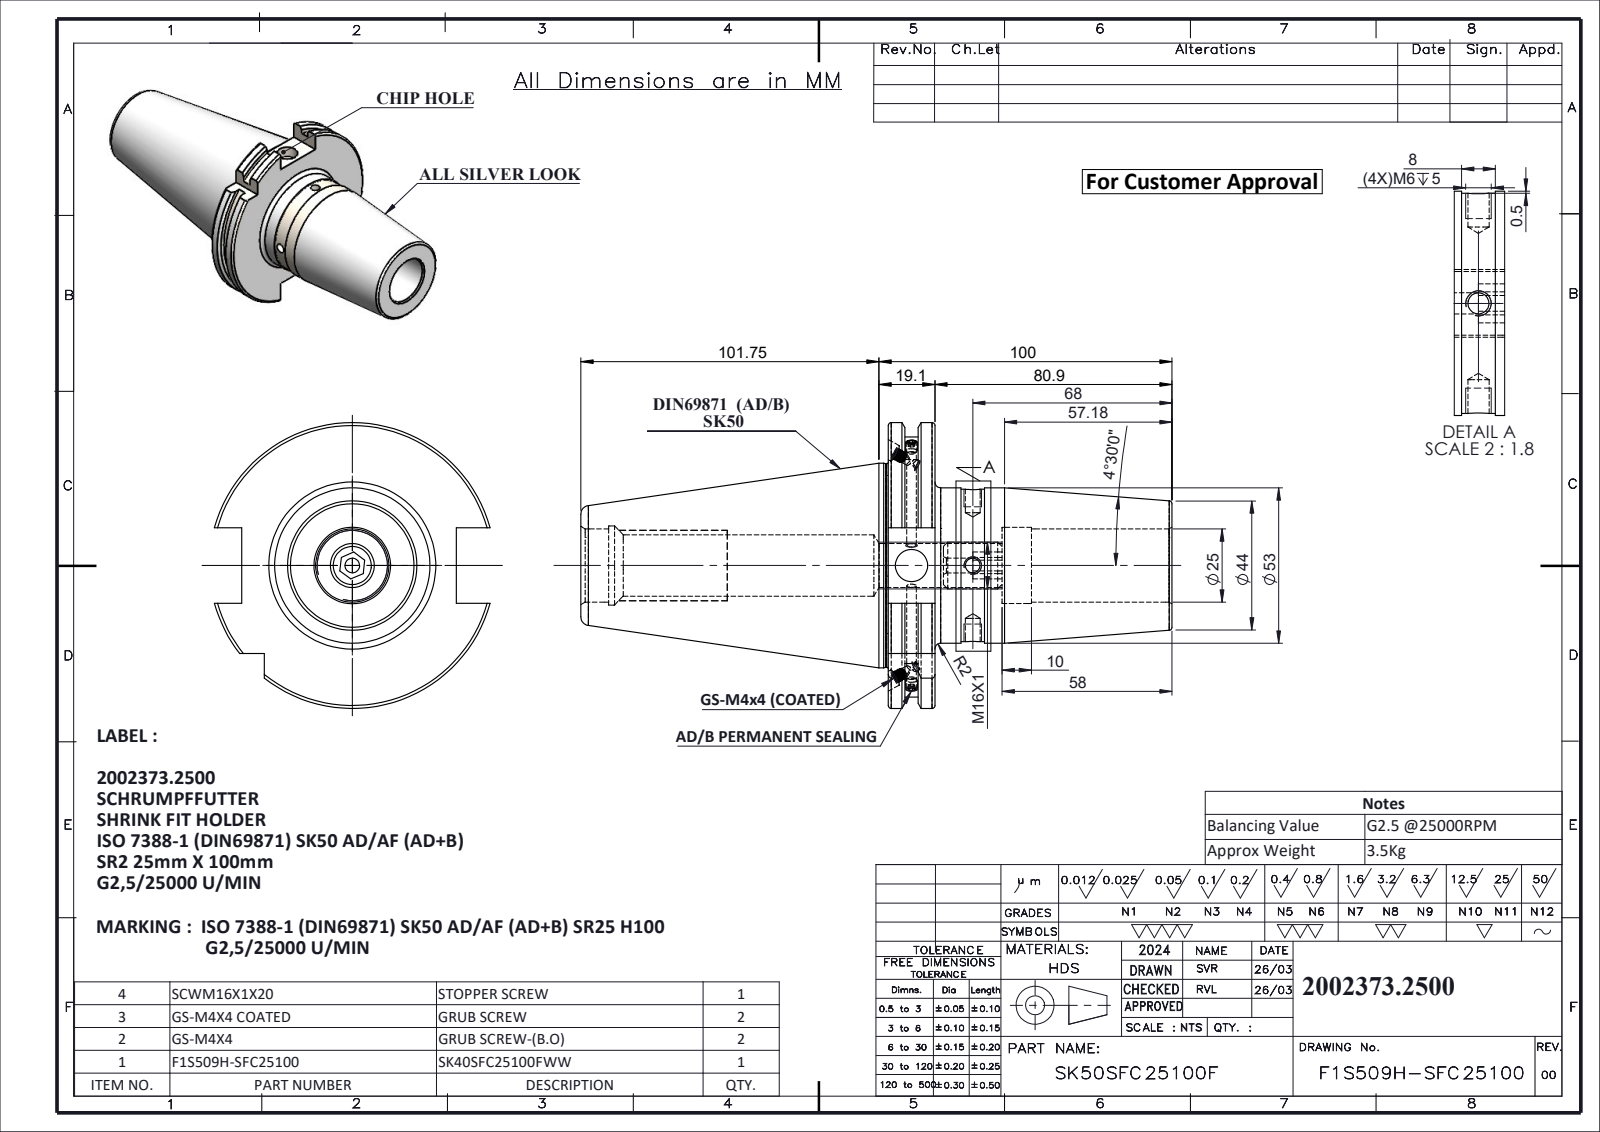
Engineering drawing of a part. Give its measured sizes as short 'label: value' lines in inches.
name: SCWM16X1P; GS-M4X4-COATING_DIN 913 - M4 x 4-N; F1S509H-SFC25100; SK50SFC25100FWW (+1 more)
written by: SolidWorks 2024 (CONFIG_CONTROL_DESIGN)
unit: in
bodies: 6 solids, 291 faces (74 planar, 91 cylindrical, 126 other)
size: 7.943 × 3.839 × 3.703
volume: 27.38 in³; area: 100.7 in²
holes: 3× ⌀0.197, 2× ⌀0.126, 2× ⌀0.236, 1× ⌀0.13, 1× ⌀0.433, 1× ⌀0.591, 1× ⌀0.827, 1× ⌀0.984, 1× ⌀1.024, 1× ⌀1.063
bosses: 4× ⌀0.157, 2× ⌀0.114, 1× ⌀2.75, 1× ⌀2.734, 1× ⌀2.087, 1× ⌀2.047, 1× ⌀0.63
rounds: 1× R1.768, 1× R1.919
face distances: 0.626, 3.811, 3.185, 0.222, 0.404, 3.589, 0.399, 0.177, 0.227, 3.412
hole spacings: 0.823
